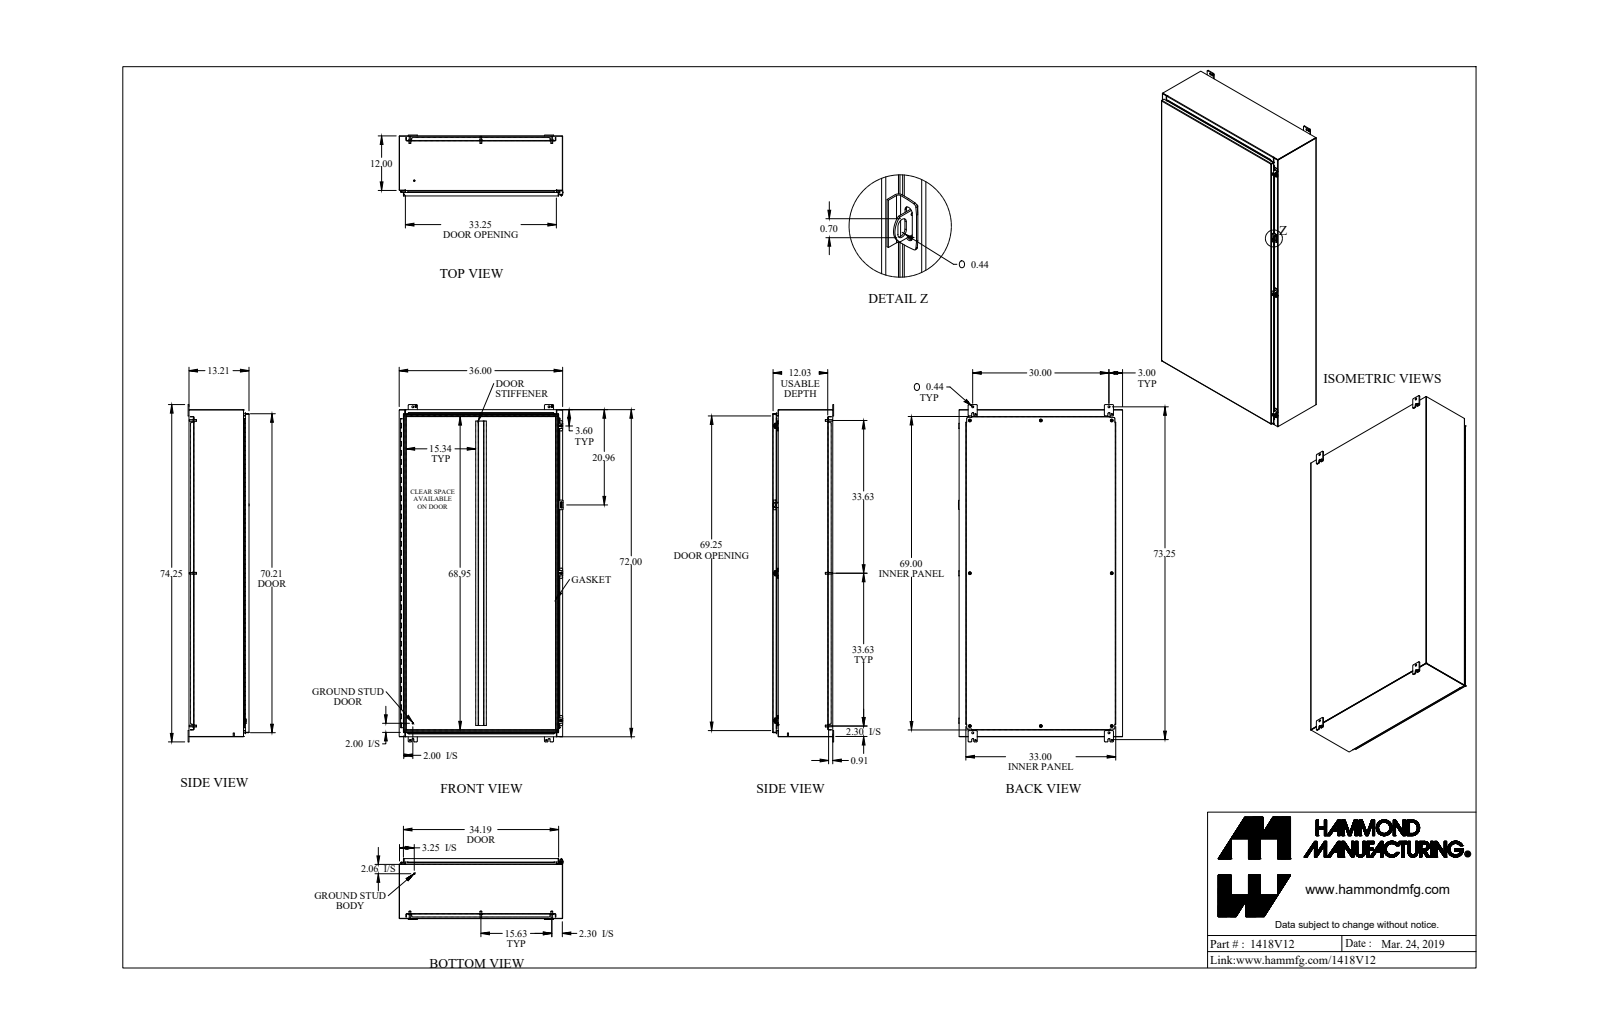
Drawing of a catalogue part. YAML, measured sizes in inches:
part_name: "1418V12_Default"
step_written_by: "SolidWorks 2019 (CONFIG_CONTROL_DESIGN)"
units: inches
bodies: {solids: 52, faces: 1894, planar: 1024, cylindrical: 794, other: 76}
overall_size: [74.25, 36.128, 13.437]
volume: 902.5
surface_area: 23226
round_holes:
  - {diameter: 0.304, count: 12}
  - {diameter: 0.5, count: 8}
  - {diameter: 0.307, count: 4}
  - {diameter: 0.313, count: 4}
  - {diameter: 0.437, count: 4}
  - {diameter: 0.445, count: 4}
  - {diameter: 0.213, count: 3}
  - {diameter: 0.265, count: 3}
  - {diameter: 0.375, count: 3}
  - {diameter: 0.11, count: 1}
  - {diameter: 0.125, count: 1}
round_bosses_or_shafts:
  - {diameter: 0.65, count: 8}
  - {diameter: 0.375, count: 8}
  - {diameter: 0.33, count: 8}
  - {diameter: 1, count: 4}
  - {diameter: 0.5, count: 3}
  - {diameter: 0.39, count: 3}
  - {diameter: 0.244, count: 3}
  - {diameter: 0.281, count: 2}
partial_cylinders:
  - {radius: 0.188, count: 38}
  - {radius: 0.036, count: 22}
  - {radius: 0.108, count: 22}
  - {radius: 0.25, count: 20}
  - {radius: 0.048, count: 19}
  - {radius: 0.143, count: 19}
  - {radius: 0.116, count: 16}
  - {radius: 0.125, count: 8}
face_to_face_distances: [0.072, 13.113, 13.041, 13.185, 0.095, 12.081, 12.009, 1.032, 1.104, 12.176]
hole_center_spacings: [6, 12, 18, 30, 24, 36, 42, 45.904]
